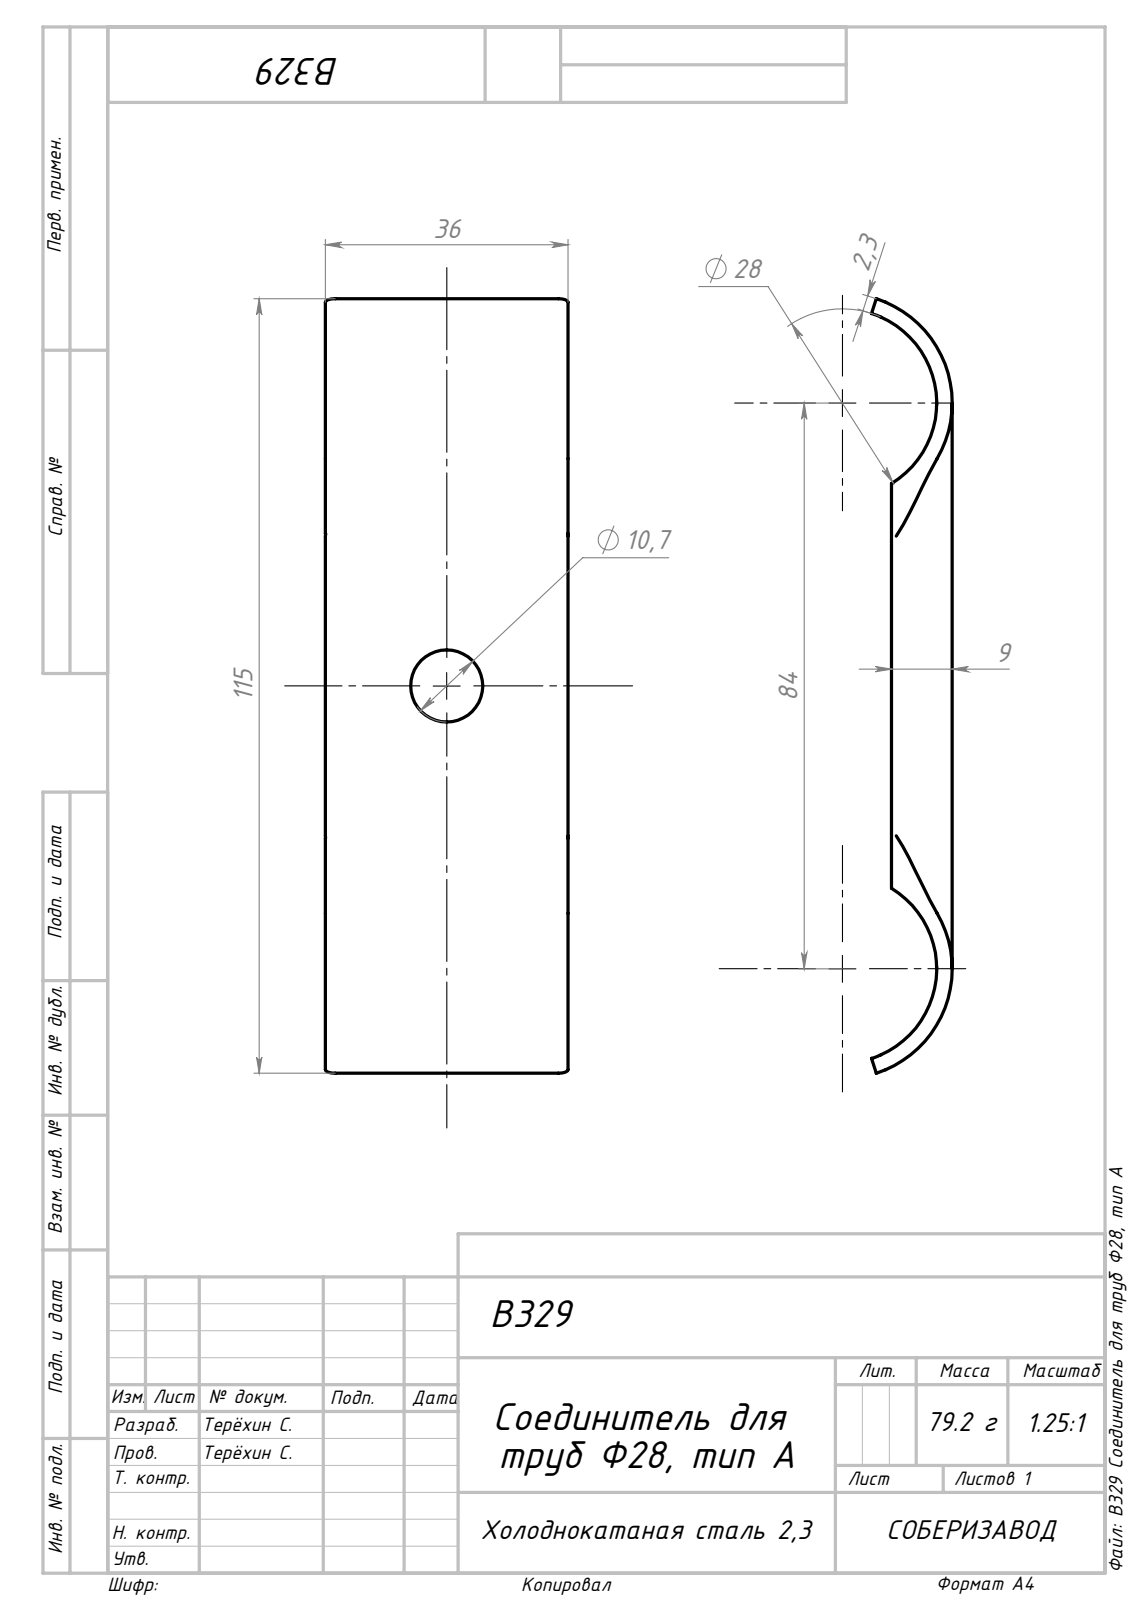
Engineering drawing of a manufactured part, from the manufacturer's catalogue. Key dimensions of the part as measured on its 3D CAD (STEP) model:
Part name (STEP PRODUCT): B329 Соединитель для труб Ф28, тип A
STEP written by: SolidWorks 2022 (AUTOMOTIVE_DESIGN)
Units: millimetres
Bodies: 1 solid, 44 faces (10 planar, 22 cylindrical, 12 other)
Overall size (bounding box): 115 × 36 × 11.97
Volume: 11 054 mm³ · Surface area: 10 379 mm²
Round holes (diameter × count): ⌀10.7 ×1
Partial cylindrical surfaces — rounded edges, fillets, slot ends (radius × count): R1.45 ×4, R6 ×2, R8.3 ×2, R14 ×2, R16.3 ×2
Main face-to-face distances: 2.3, 9, 6.7, 36, 33.7, 31.4
